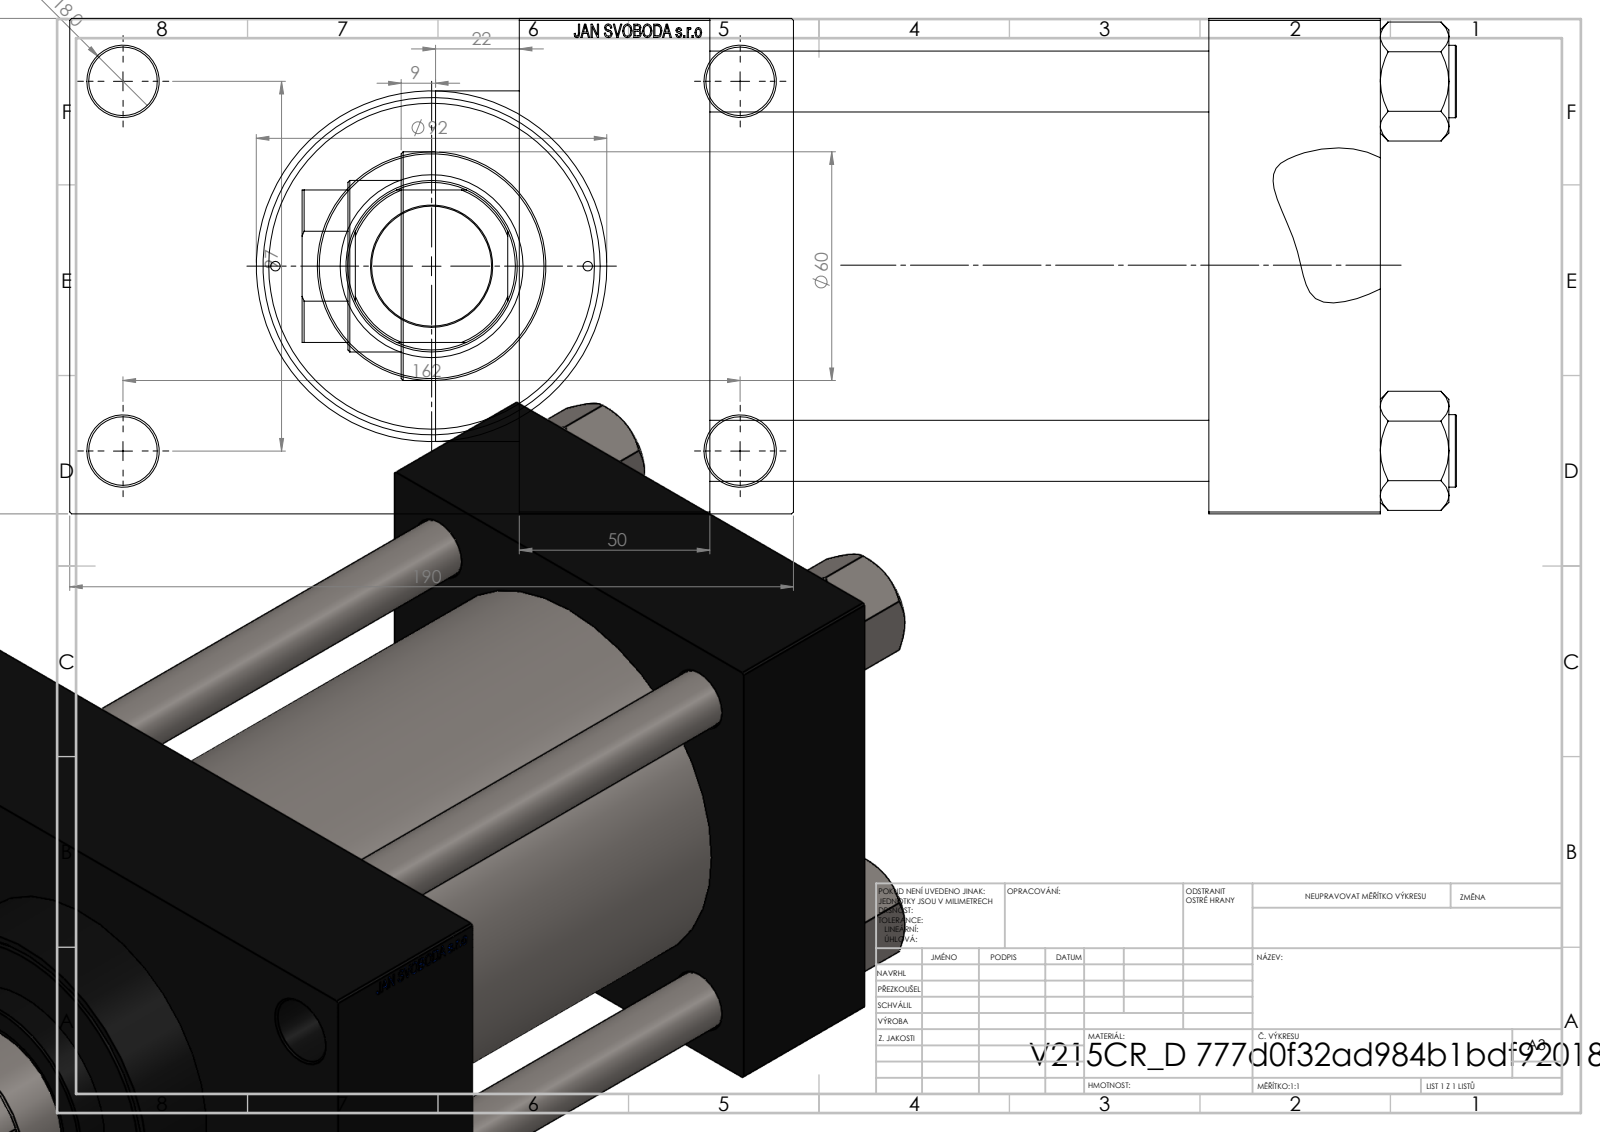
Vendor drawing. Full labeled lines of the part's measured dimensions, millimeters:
Part name (STEP PRODUCT): V215_VC_A; V215CR_D_TYCINKA; V215CR_VCP_D; V215CR_D_Body (+1 more)
STEP written by: SolidWorks 2019 (CONFIG_CONTROL_DESIGN)
Units: millimetres
Bodies: 11 solids, 1159 faces (547 planar, 92 cylindrical, 520 other)
Overall size (bounding box): 303 × 190 × 130
Volume: 2 792 000 mm³ · Surface area: 414 099 mm²
Round holes (diameter × count): ⌀16 ×4, ⌀18 ×4, ⌀2.5 ×2, ⌀7 ×2, ⌀26.44 ×2, ⌀35 ×2, ⌀31.5 ×1, ⌀45 ×1, ⌀48 ×1, ⌀76 ×1, ⌀85.5 ×1, ⌀100 ×1
Round bosses / shafts (diameter × count): ⌀19 ×4, ⌀106 ×1, ⌀92 ×1, ⌀60 ×1
Partial cylindrical surfaces — rounded edges, fillets, slot ends (radius × count): R22 ×1
Main face-to-face distances: 130, 45, 176, 131, 226, 181, 50, 30, 160, 80
Hole centre spacings: 32.55, 49.02, 62.87, 68.52, 94.41, 96.9, 101.73, 102.27
